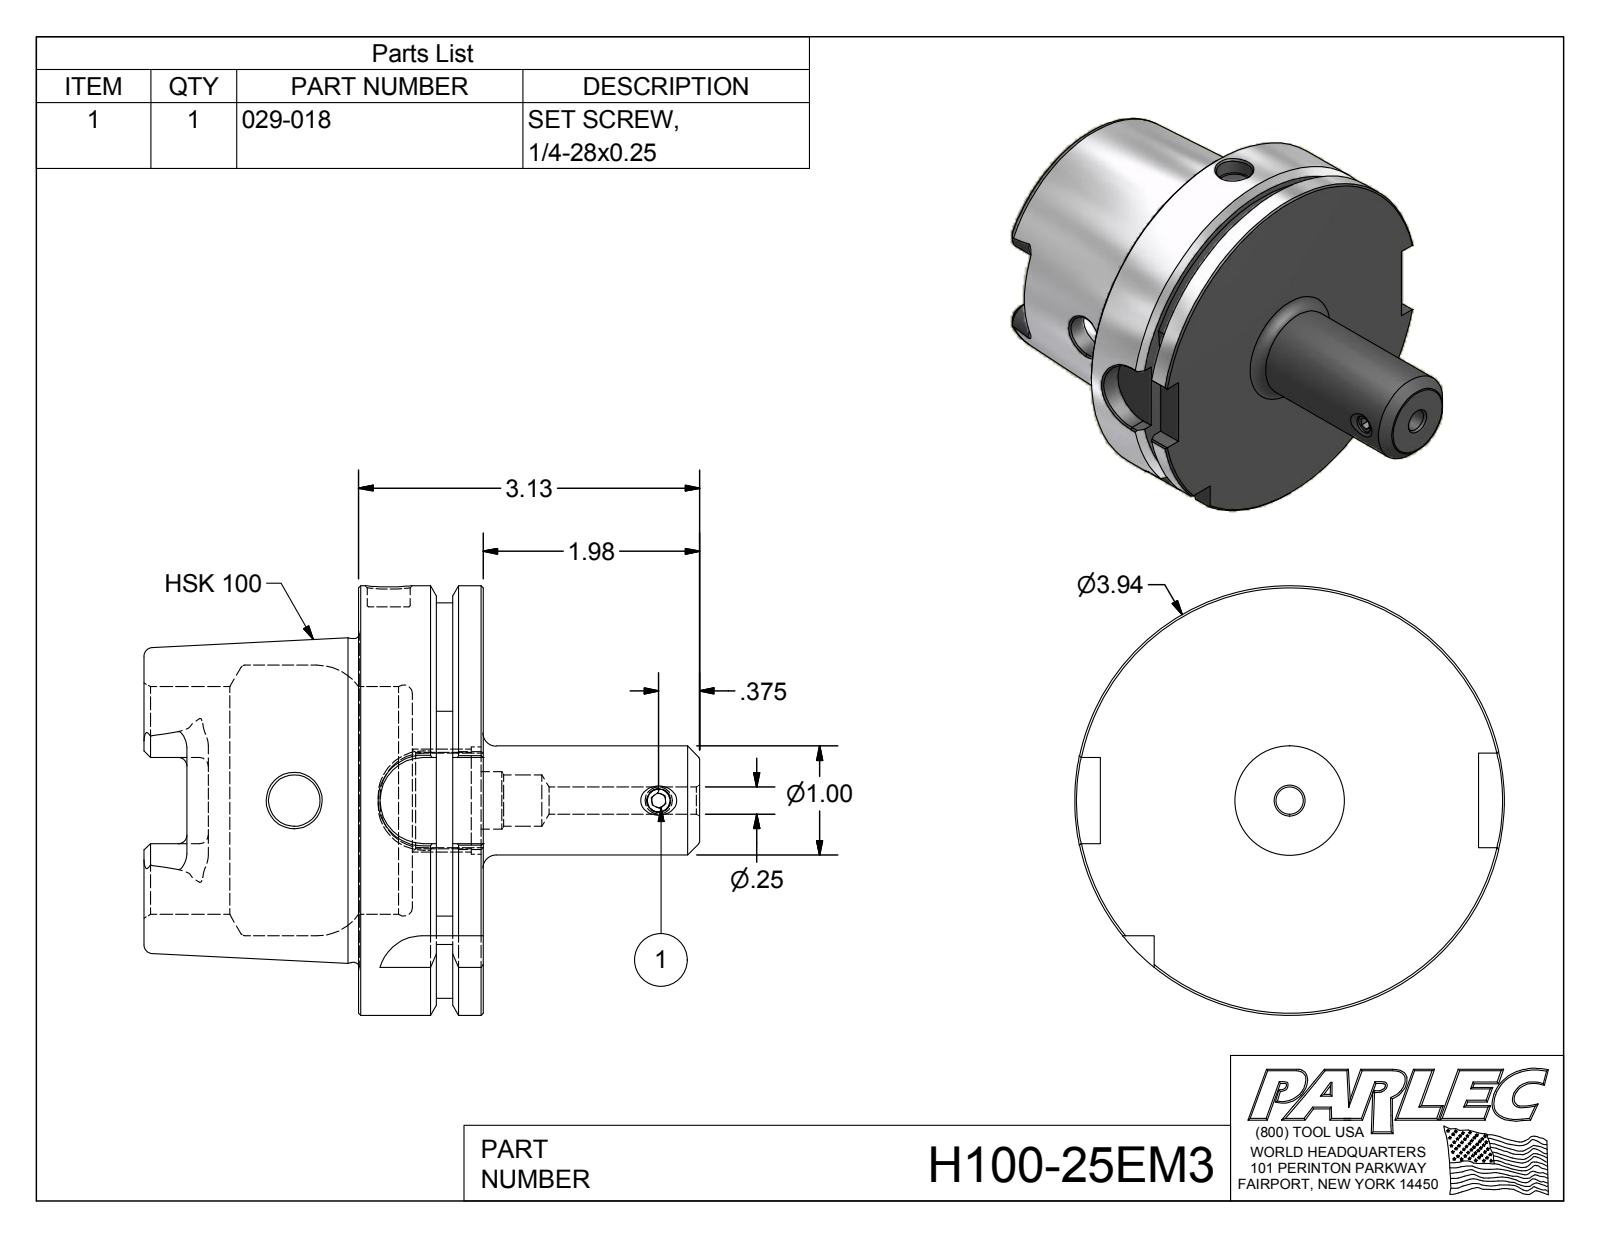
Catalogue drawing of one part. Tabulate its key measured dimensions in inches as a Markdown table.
| quantity | value |
| --- | --- |
| part name | H100-25EM3; H100-25EM3-1; 029-018 |
| STEP written by | Autodesk Inventor 2012 (AUTOMOTIVE_DESIGN) |
| units | inches |
| bodies | 2 solids, 142 faces (52 planar, 37 cylindrical, 53 other) |
| overall size | 5.094 × 3.937 × 3.937 |
| volume | 16.85 in³ |
| surface area | 85.79 in² |
| round holes (diameter × count) | 0.209 × 1, 0.211 × 1, 0.25 × 1, 0.394 × 1, 0.472 × 1, 0.472 × 1, 0.527 × 1, 0.881 × 1, 0.985 × 1, 2.087 × 1, 2.48 × 1 |
| round bosses / shafts (diameter × count) | 3.937 × 1, 2.967 × 1, 1 × 1, 0.25 × 1 |
| partial cylindrical surfaces (radius × count) | 0.079 × 6, 0.192 × 4, 0.394 × 4, 1.811 × 1 |
| main face-to-face distances | 1.142, 0.492, 0.65, 1.969, 2.461, 3.11, 2.83, 0.861, 0.369, 0.28 |
| hole center spacings | 3.341 |
